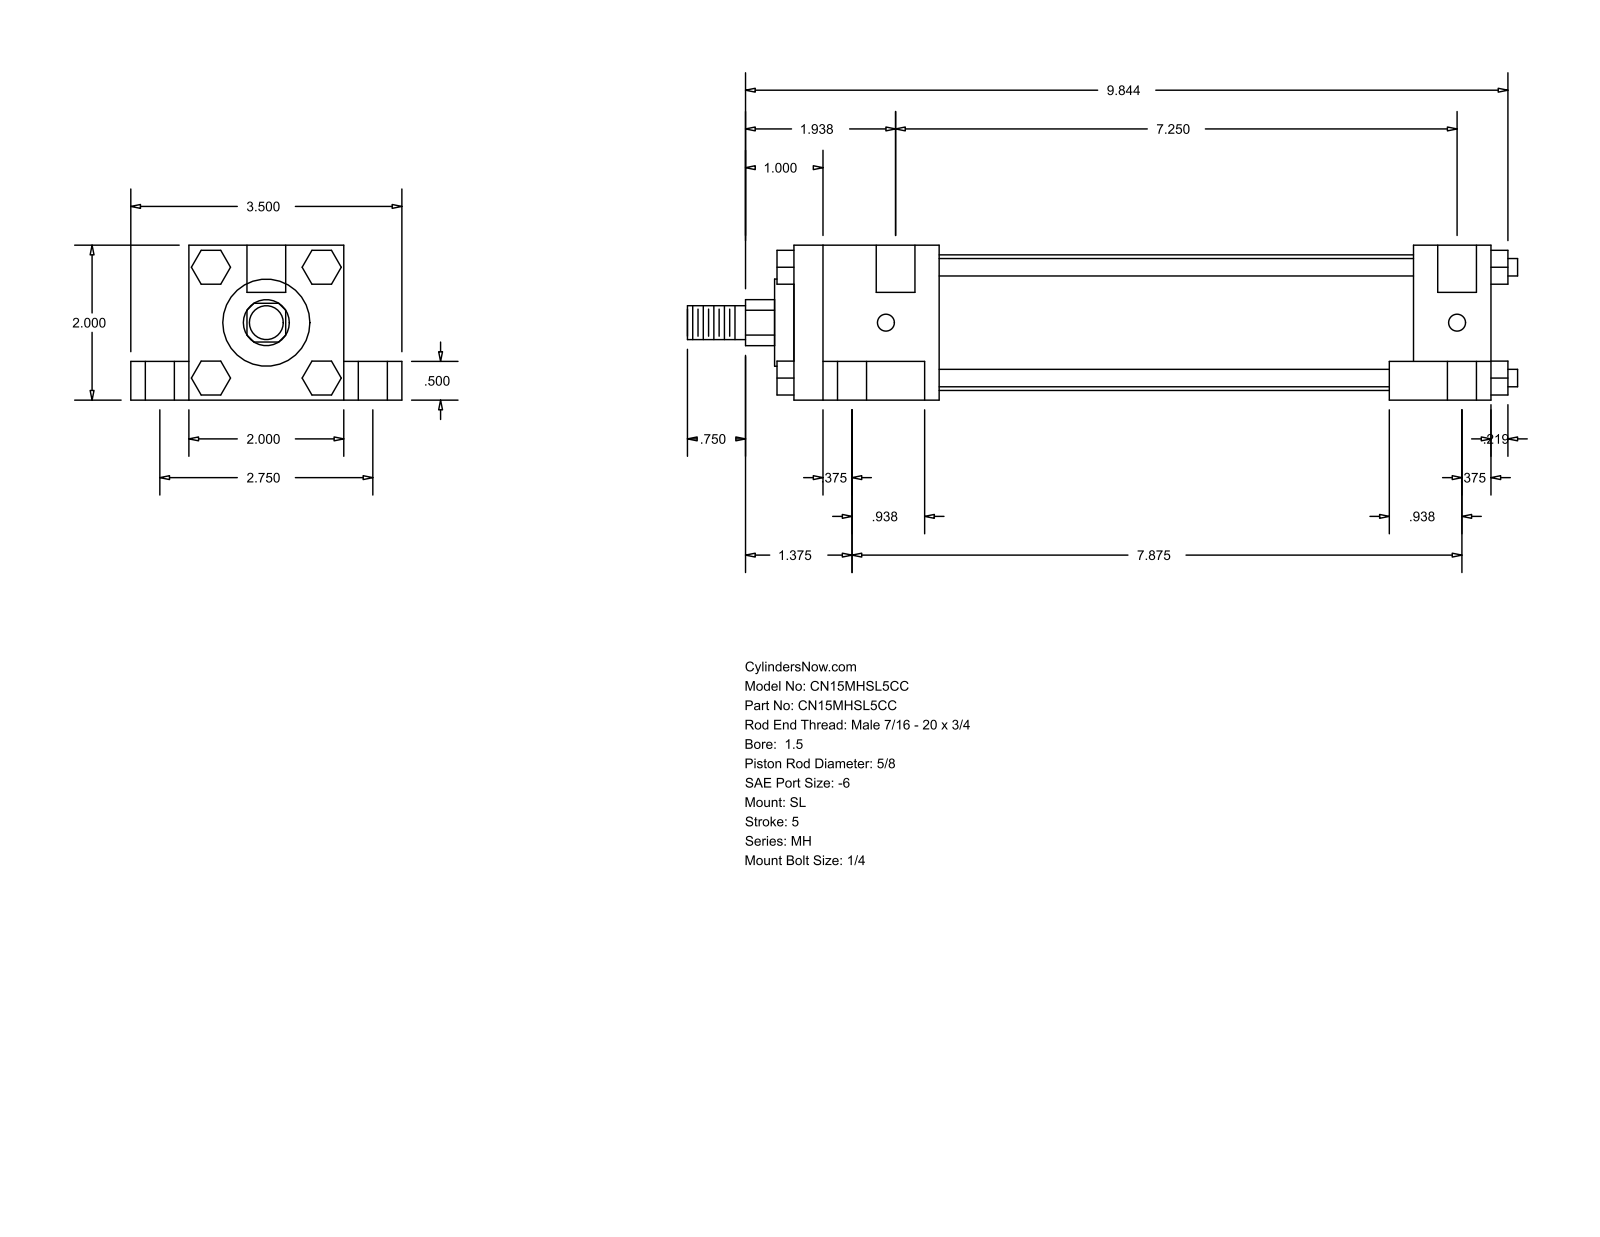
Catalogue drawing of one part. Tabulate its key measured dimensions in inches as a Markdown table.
| quantity | value |
| --- | --- |
| part name | MH_SL__0150_0.625 |
| STEP written by | GSSL Pune (CONFIG_CONTROL_DESIGN) |
| units | inches |
| bodies | 0 solids, 148 faces (112 planar, 36 cylindrical, 0 other) |
| overall size | 10.719 × 3.5 × 2 |
| round holes (diameter × count) | 0.219 × 4, 0.375 × 4, 0.625 × 4, 0.5 × 2 |
| round bosses / shafts (diameter × count) | 0.225 × 4, 1.75 × 1, 1.125 × 1, 0.625 × 1, 0.437 × 1 |
| partial cylindrical surfaces (radius × count) | 0.297 × 1 |
| main face-to-face distances | 2, 1.5, 0.75, 0.5, 2.75, 9, 1, 0.375, 8, 1.875 |
| hole center spacings | 1.376, 1.443, 1.485, 2.75, 7.375, 7.441, 7.563, 7.875 |
